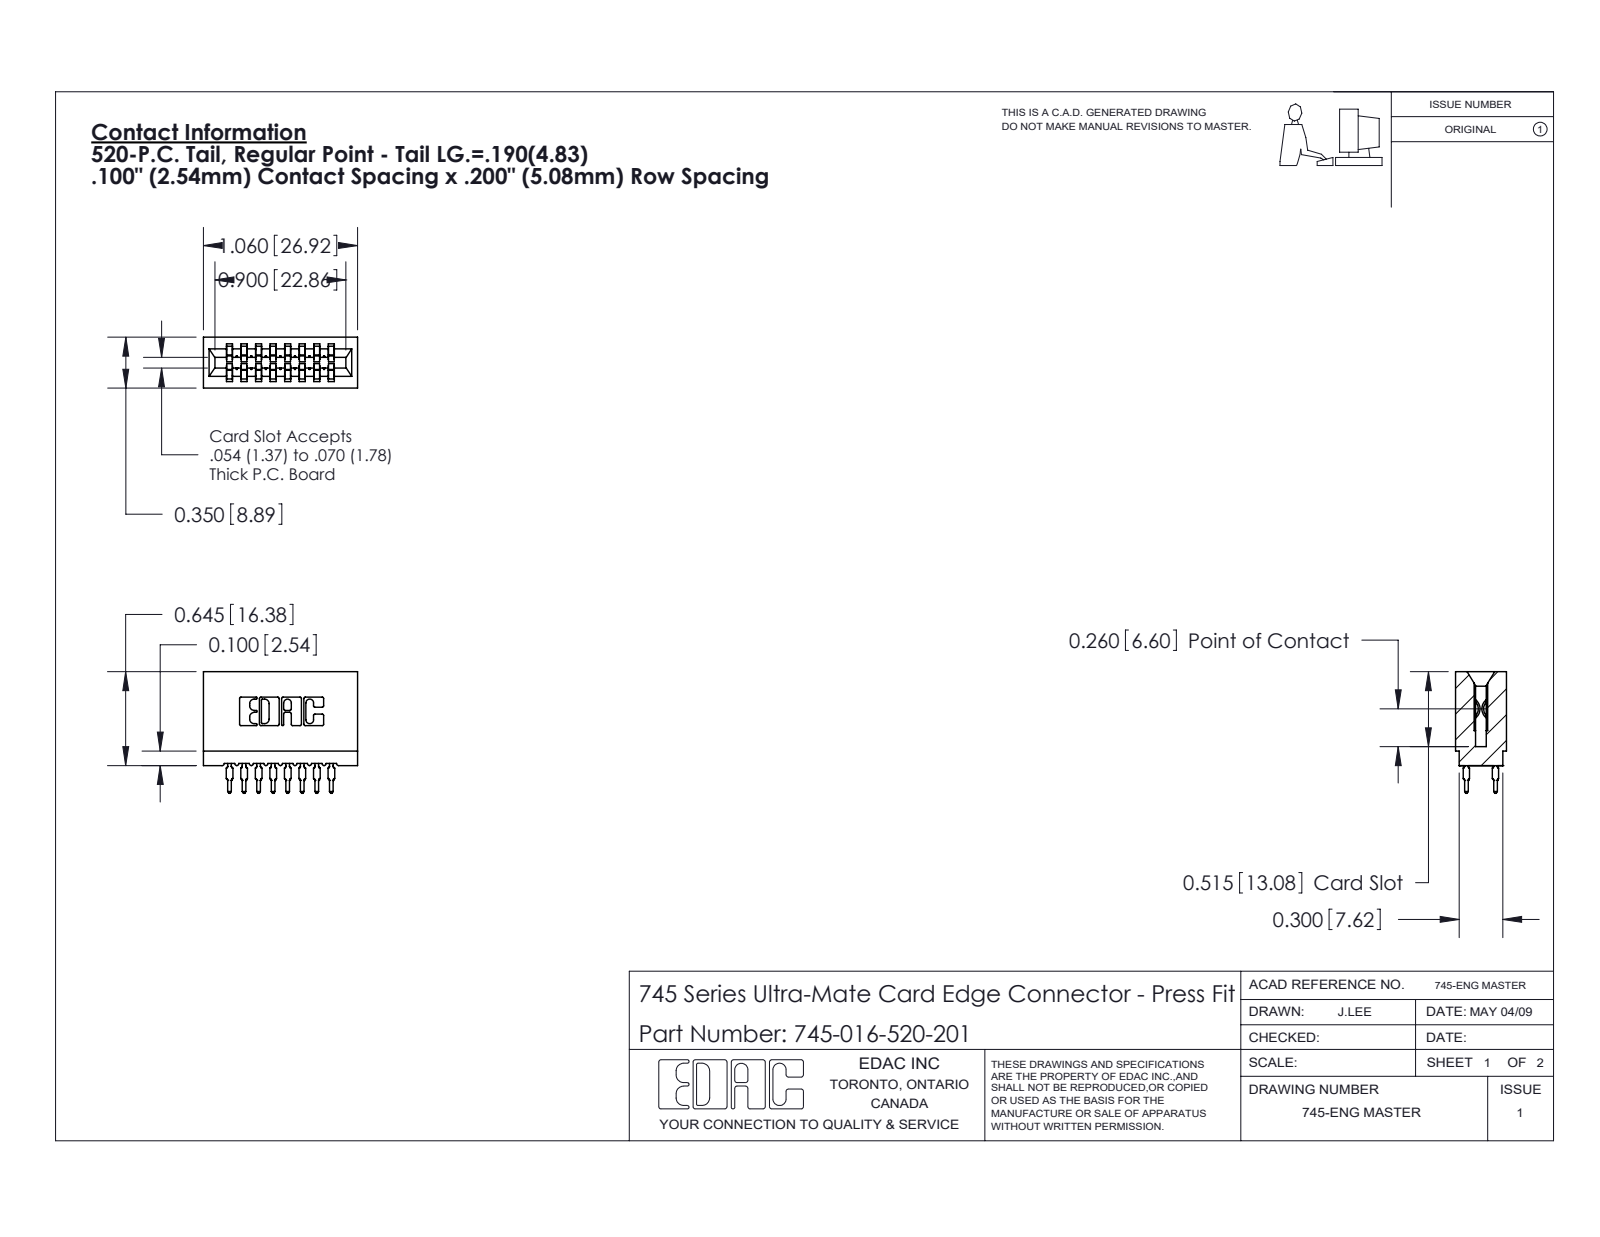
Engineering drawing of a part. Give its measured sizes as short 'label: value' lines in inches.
name: 745-292-001_520; 745 Part_Insulator Option - 01; 745-016-520-201
written by: SolidWorks 2020 (CONFIG_CONTROL_DESIGN)
unit: in
bodies: 17 solids, 1527 faces (791 planar, 320 cylindrical, 416 other)
size: 1.06 × 0.836 × 0.35
volume: 0.16 in³; area: 6.911 in²
rounds: 32× R0.021, 22× R0.01, 16× R0.015, 8× R0.005, 8× R0.011, 6× R0.007, 6× R0.031, 3× R0.026
face distances: 0.1, 0.2, 0.3, 0.042, 0.4, 0.142, 0.058, 0.242, 0.5, 0.158
